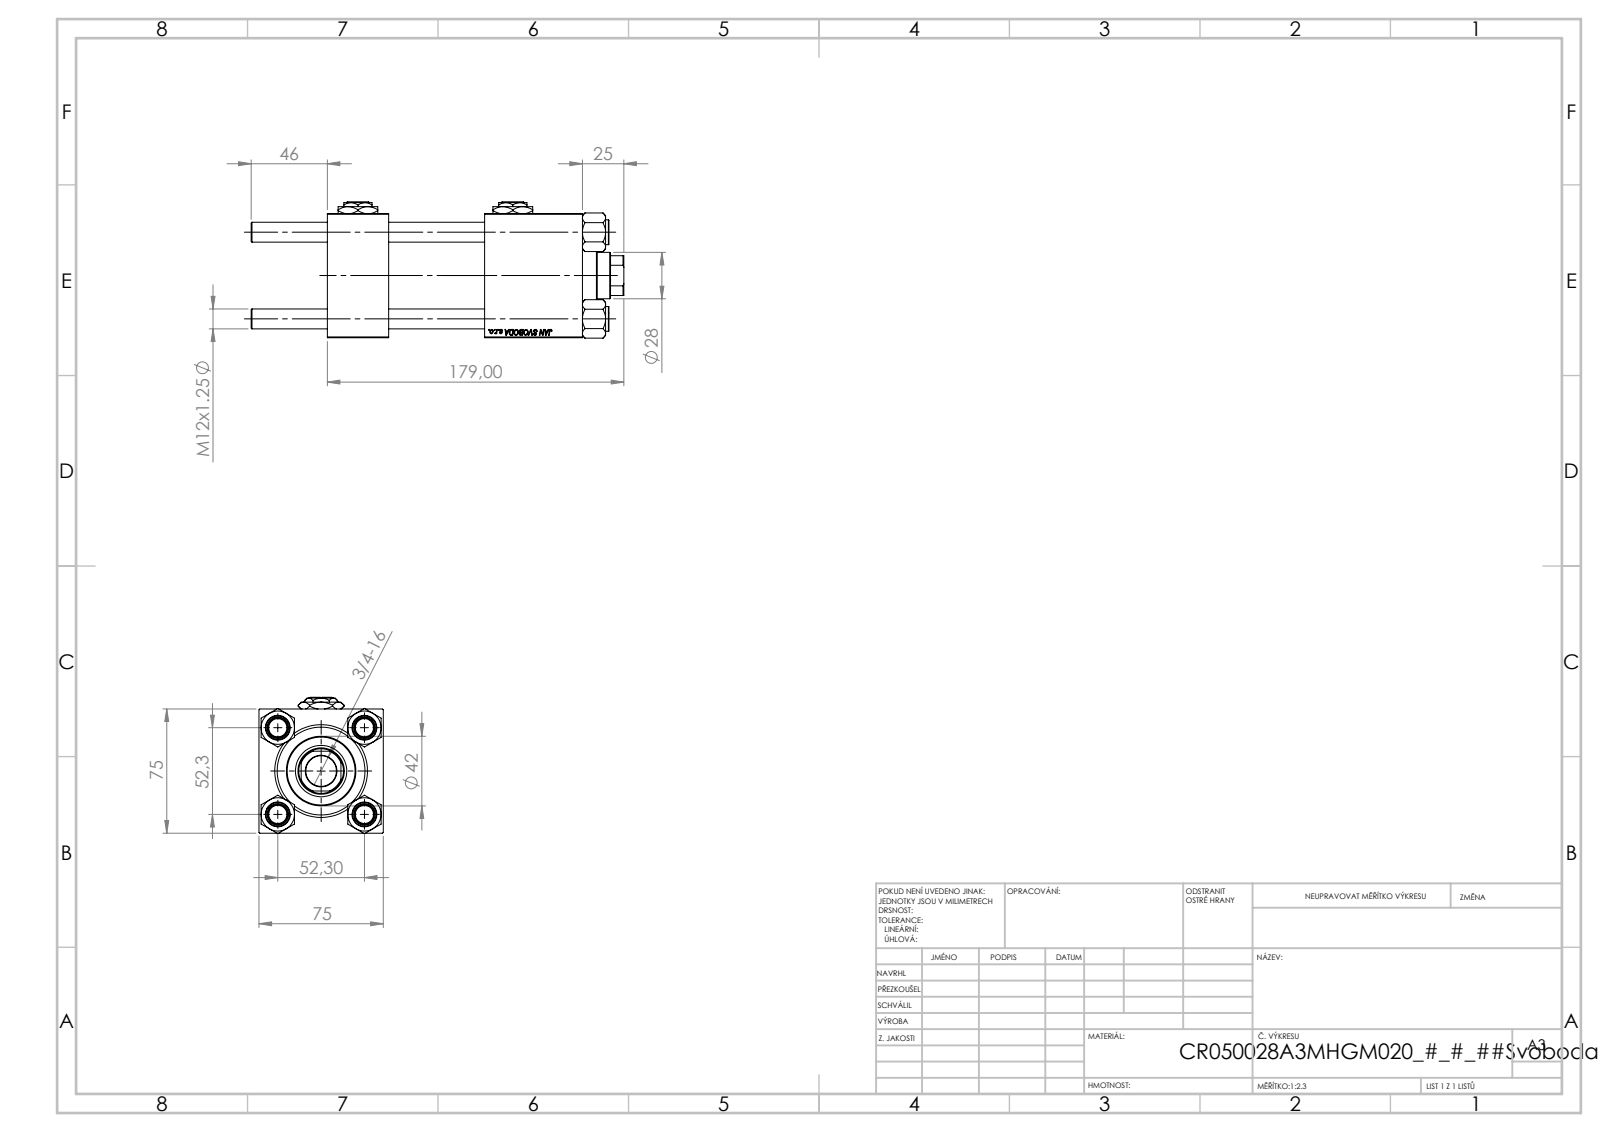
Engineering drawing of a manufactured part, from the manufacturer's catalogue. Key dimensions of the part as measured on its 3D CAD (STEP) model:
Part name (STEP PRODUCT): NUT_M5; Zatka_pro_OIL_PORT; V215_VC_A; V215CR_BODY_A (+2 more)
STEP written by: SolidWorks 2019 (CONFIG_CONTROL_DESIGN)
Units: millimetres
Bodies: 13 solids, 1233 faces (567 planar, 88 cylindrical, 578 other)
Overall size (bounding box): 225 × 82.27 × 75
Volume: 697 084 mm³ · Surface area: 171 866 mm²
Round holes (diameter × count): ⌀12 ×4, ⌀7 ×2, ⌀20.96 ×2, ⌀30 ×2, ⌀18.5 ×1, ⌀28 ×1, ⌀31 ×1, ⌀41 ×1, ⌀50 ×1, ⌀53 ×1
Round bosses / shafts (diameter × count): ⌀15 ×4, ⌀56 ×1, ⌀42 ×1
Partial cylindrical surfaces — rounded edges, fillets, slot ends (radius × count): R13.5 ×1
Main face-to-face distances: 75, 37, 154, 117, 95, 59, 58, 125.3, 88.3, 30.3
Hole centre spacings: 36.98, 52.3, 73.96, 93.5
